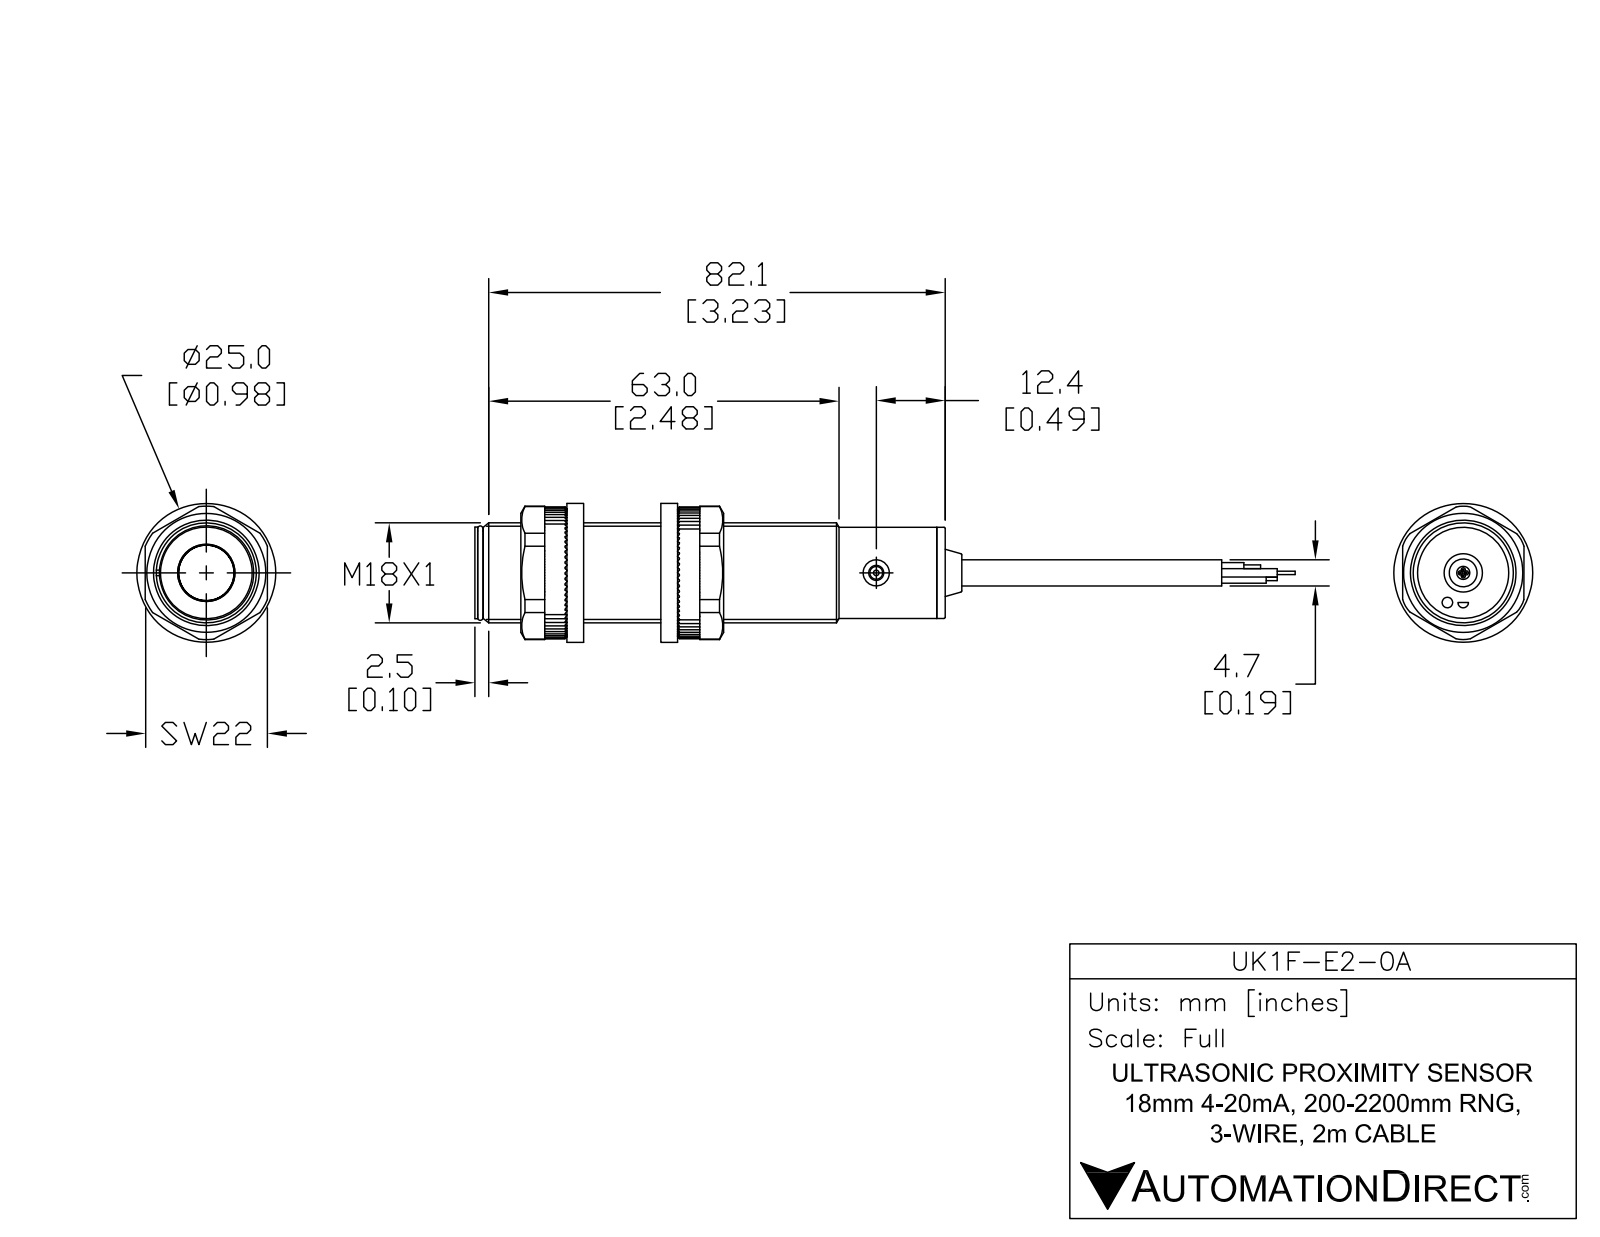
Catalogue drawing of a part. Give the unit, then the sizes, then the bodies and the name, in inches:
Units: inches
Overall size (bounding box): 4.832 × 0.709 × 0.709
Round holes (diameter × count): ⌀0.185 ×2, ⌀0.106 ×1
Round bosses / shafts (diameter × count): ⌀0.709 ×1, ⌀0.646 ×1, ⌀0.622 ×1, ⌀0.374 ×1, ⌀0.189 ×1, ⌀0.091 ×1
Main face-to-face distances: 3.193, 3.252, 0.059, 0.039, 3.232, 3.291, 0.041, 3.234, 3.293, 3.257
Volume: 1.285 in³ · Surface area: 10.69 in²
Bodies: 6 solids, 55 faces (17 planar, 24 cylindrical, 14 other)
Part name (STEP PRODUCT): UK1F-E2-0A
STEP written by: SolidWorks 2017 (AUTOMOTIVE_DESIGN)
